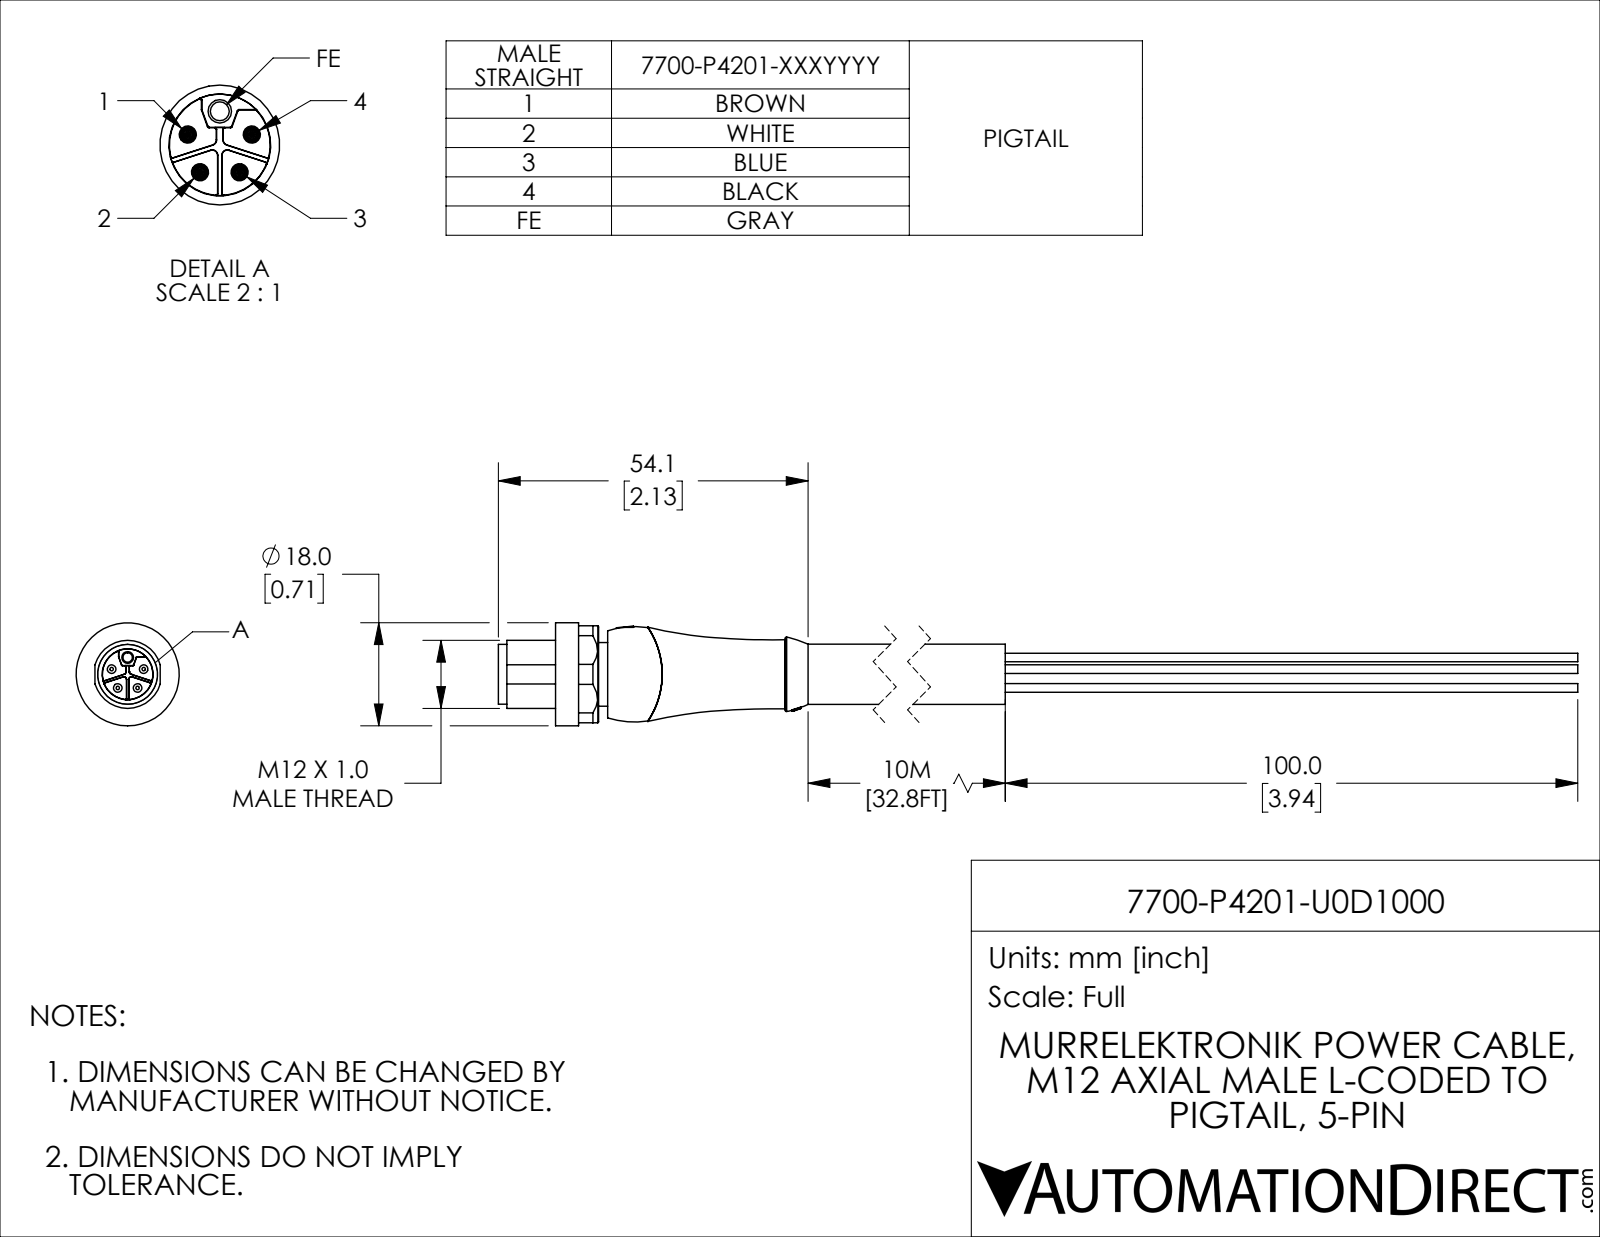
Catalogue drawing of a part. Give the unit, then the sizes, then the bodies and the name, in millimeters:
Units: millimetres
Overall size (bounding box): 254.1 × 18 × 18
Round holes (diameter × count): ⌀1.65 ×1
Round bosses / shafts (diameter × count): ⌀1.5 ×5, ⌀18 ×1, ⌀11.88 ×1, ⌀11.1 ×1, ⌀10.5 ×1, ⌀10.45 ×1
Partial cylindrical surfaces — rounded edges, fillets, slot ends (radius × count): R0.15 ×6, R1.13 ×1, R8.95 ×1
Main face-to-face distances: 9.1, 1.9, 7.2, 144.1, 136.9, 135, 16.94, 1.2, 8.4, 10.3
Volume: 17 489 mm³ · Surface area: 9 110 mm²
Bodies: 1 solid, 190 faces (87 planar, 51 cylindrical, 52 other)
Part name (STEP PRODUCT): 7700-P4201-U0D1000
STEP written by: SolidWorks 2021 (CONFIG_CONTROL_DESIGN)
